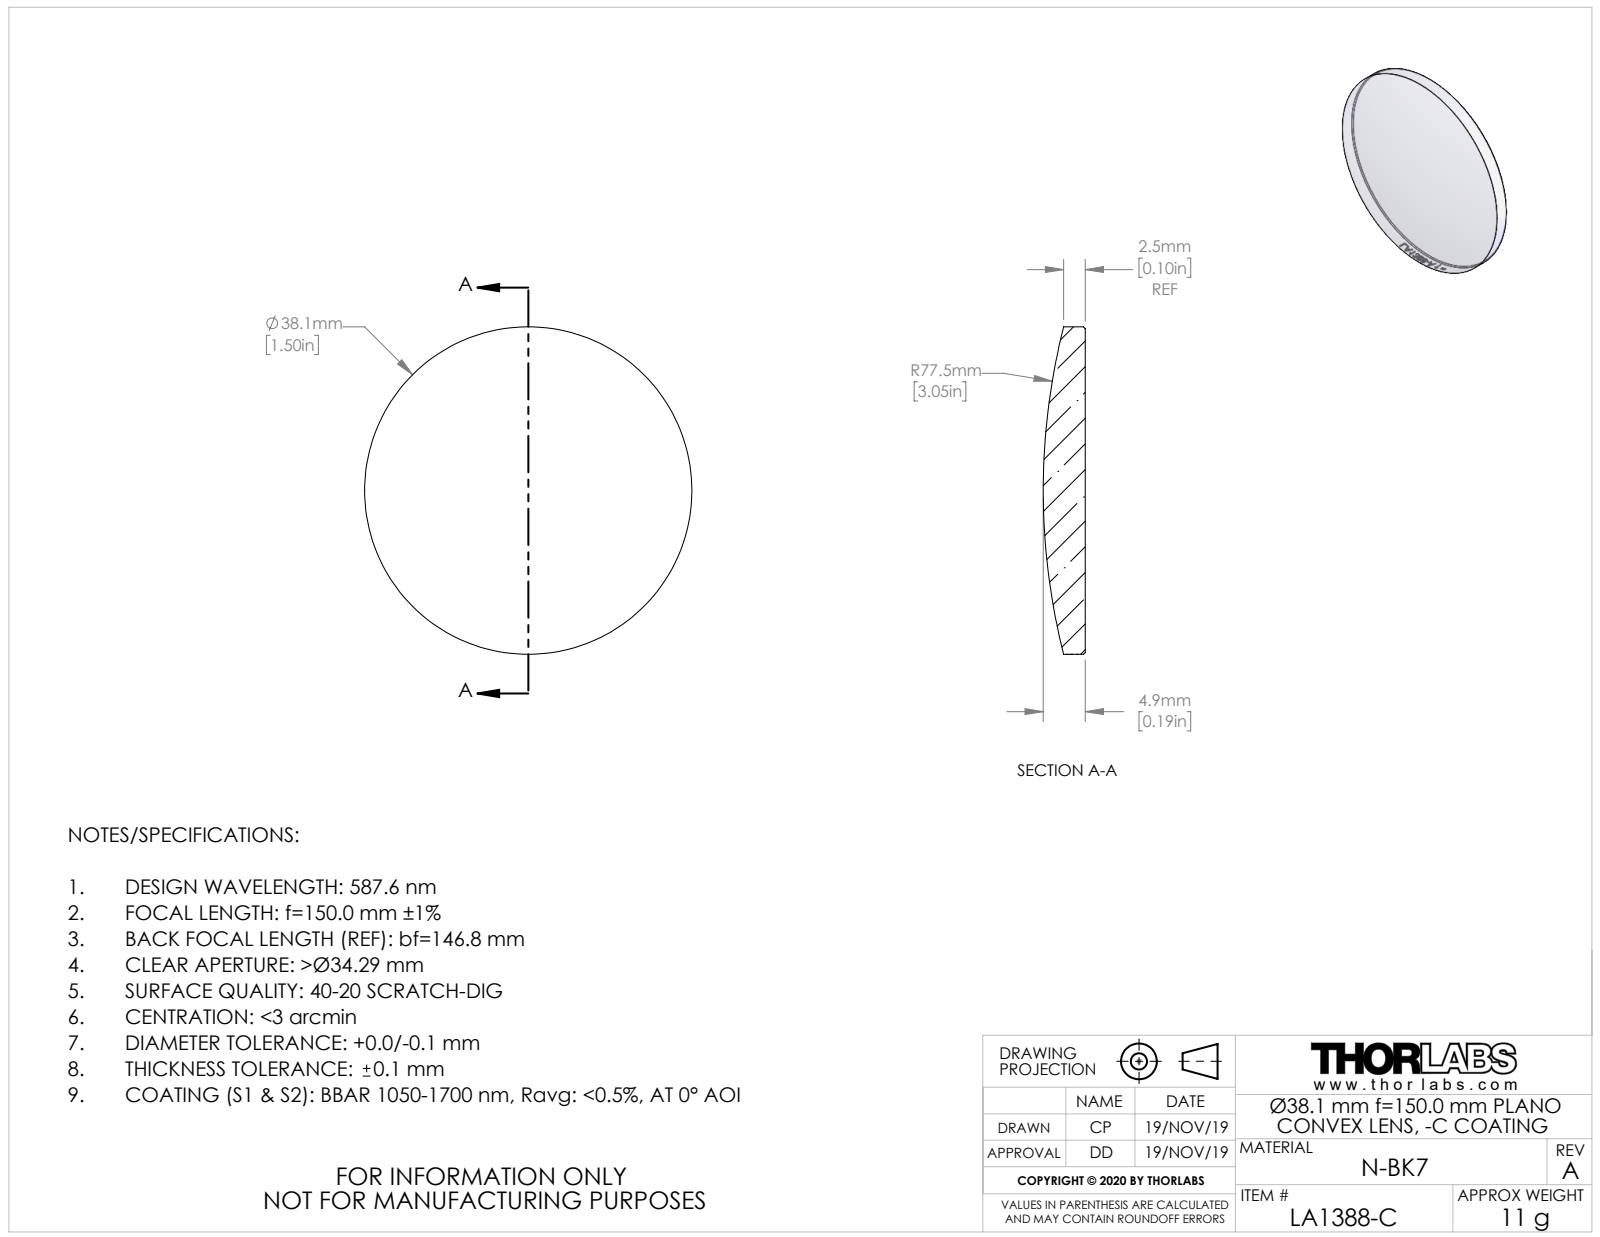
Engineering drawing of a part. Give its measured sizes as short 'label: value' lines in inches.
name: TTN200742-E0W
written by: SolidWorks 2018 (CONFIG_CONTROL_DESIGN)
unit: in
bodies: 1 solid, 25 faces (1 planar, 20 cylindrical, 4 other)
size: 1.5 × 1.5 × 0.192
volume: 0.257 in³; area: 4.004 in²
bosses: 1× ⌀1.5
